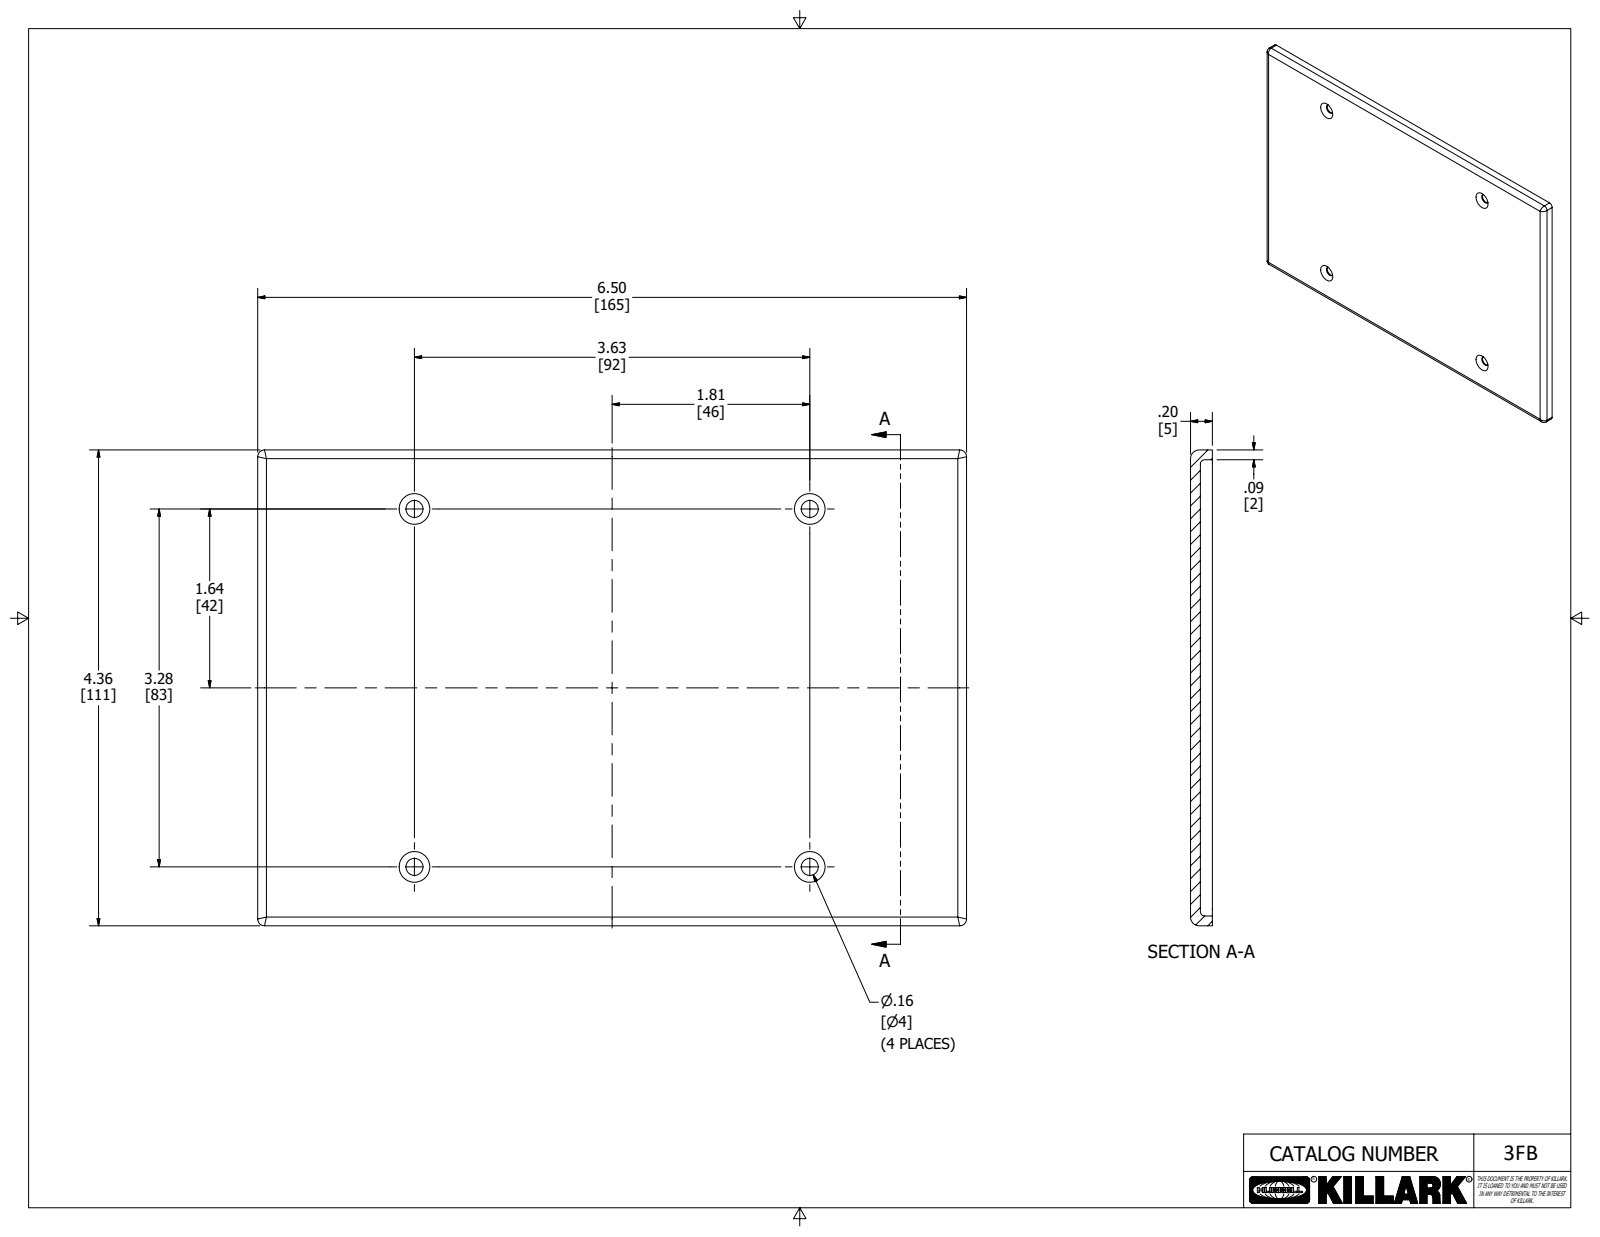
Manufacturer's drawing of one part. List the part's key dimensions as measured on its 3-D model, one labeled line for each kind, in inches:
Part name (STEP PRODUCT): 07806-2
STEP written by: Autodesk Inventor 2020 (AUTOMOTIVE_DESIGN)
Units: inches
Bodies: 1 solid, 43 faces (11 planar, 20 cylindrical, 12 other)
Overall size (bounding box): 6.5 × 4.362 × 0.2
Volume: 2.728 in³ · Surface area: 62.19 in²
Round holes (diameter × count): ⌀0.156 ×4
Partial cylindrical surfaces — rounded edges, fillets, slot ends (radius × count): R0.062 ×6, R0.04 ×4, R0.08 ×4, R0.031 ×2
Main face-to-face distances: 0.09, 0.11, 0.2, 4.272, 4.362, 6.41, 6.5, 4.182, 6.32
Hole centre spacings: 3.281, 3.625, 4.889
